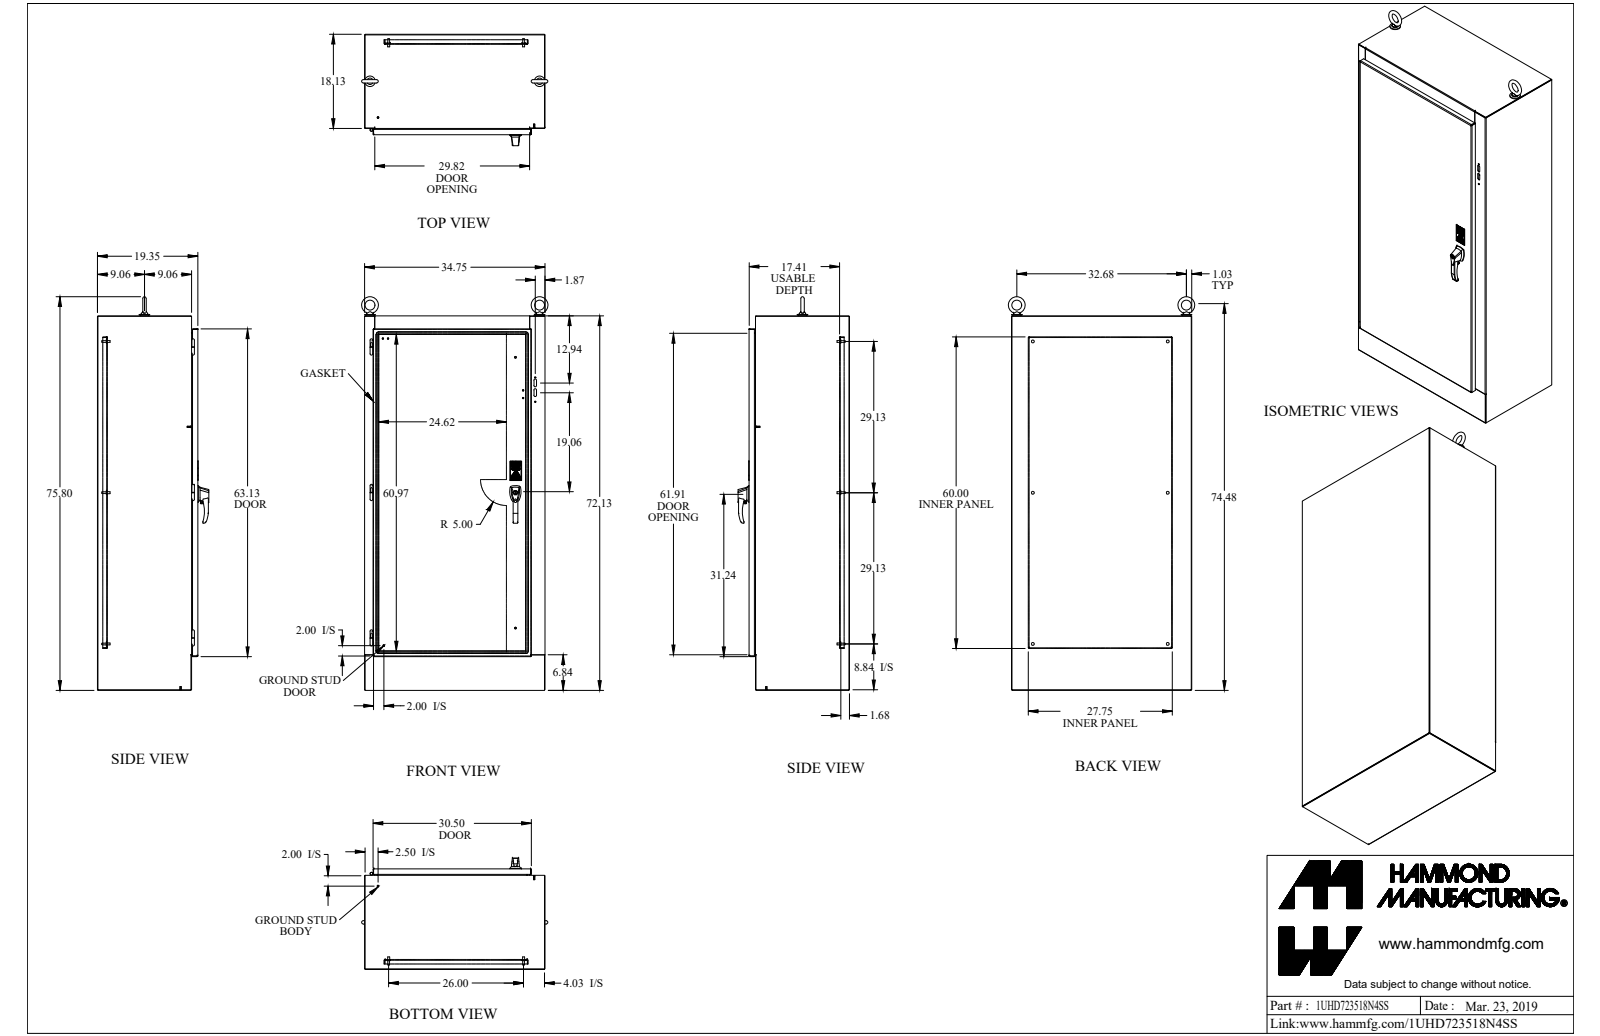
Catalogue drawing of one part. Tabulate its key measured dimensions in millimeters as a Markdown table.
| quantity | value |
| --- | --- |
| part name | 1UHD723518N4SS |
| STEP written by | SolidWorks 2018 (AUTOMOTIVE_DESIGN) |
| units | millimeters |
| bodies | 112 solids, 2003 faces (1132 planar, 535 cylindrical, 336 other) |
| overall size | 1925.3 × 912.7 × 545.2 |
| volume | 20 730 000 mm³ |
| surface area | 16 280 000 mm² |
| round holes (diameter × count) | 8.9 × 7, 5 × 6, 7.8 × 6, 14.3 × 6, 6.4 × 5, 4 × 4, 7.1 × 4, 11.3 × 4, 8 × 3, 4.2 × 2, 4.8 × 2, 6.5 × 2 |
| round bosses / shafts (diameter × count) | 6.4 × 11, 25.4 × 8, 16.5 × 6, 9.5 × 6, 8.4 × 6, 4.8 × 4, 15.9 × 3, 12.7 × 3 |
| partial cylindrical surfaces (radius × count) | 3.2 × 27, 1.2 × 24, 3.6 × 24, 12.7 × 23, 1.5 × 19, 6.4 × 19, 0.4 × 16, 0.8 × 12 |
| main face-to-face distances | 2.4, 489.1, 486.6, 491.5, 3.2, 443.1, 440.6, 46, 48.4, 446.2 |
| hole center spacings | 660.4, 188.8, 189.7, 190.5, 327, 378.5, 633.4, 690.6 |
